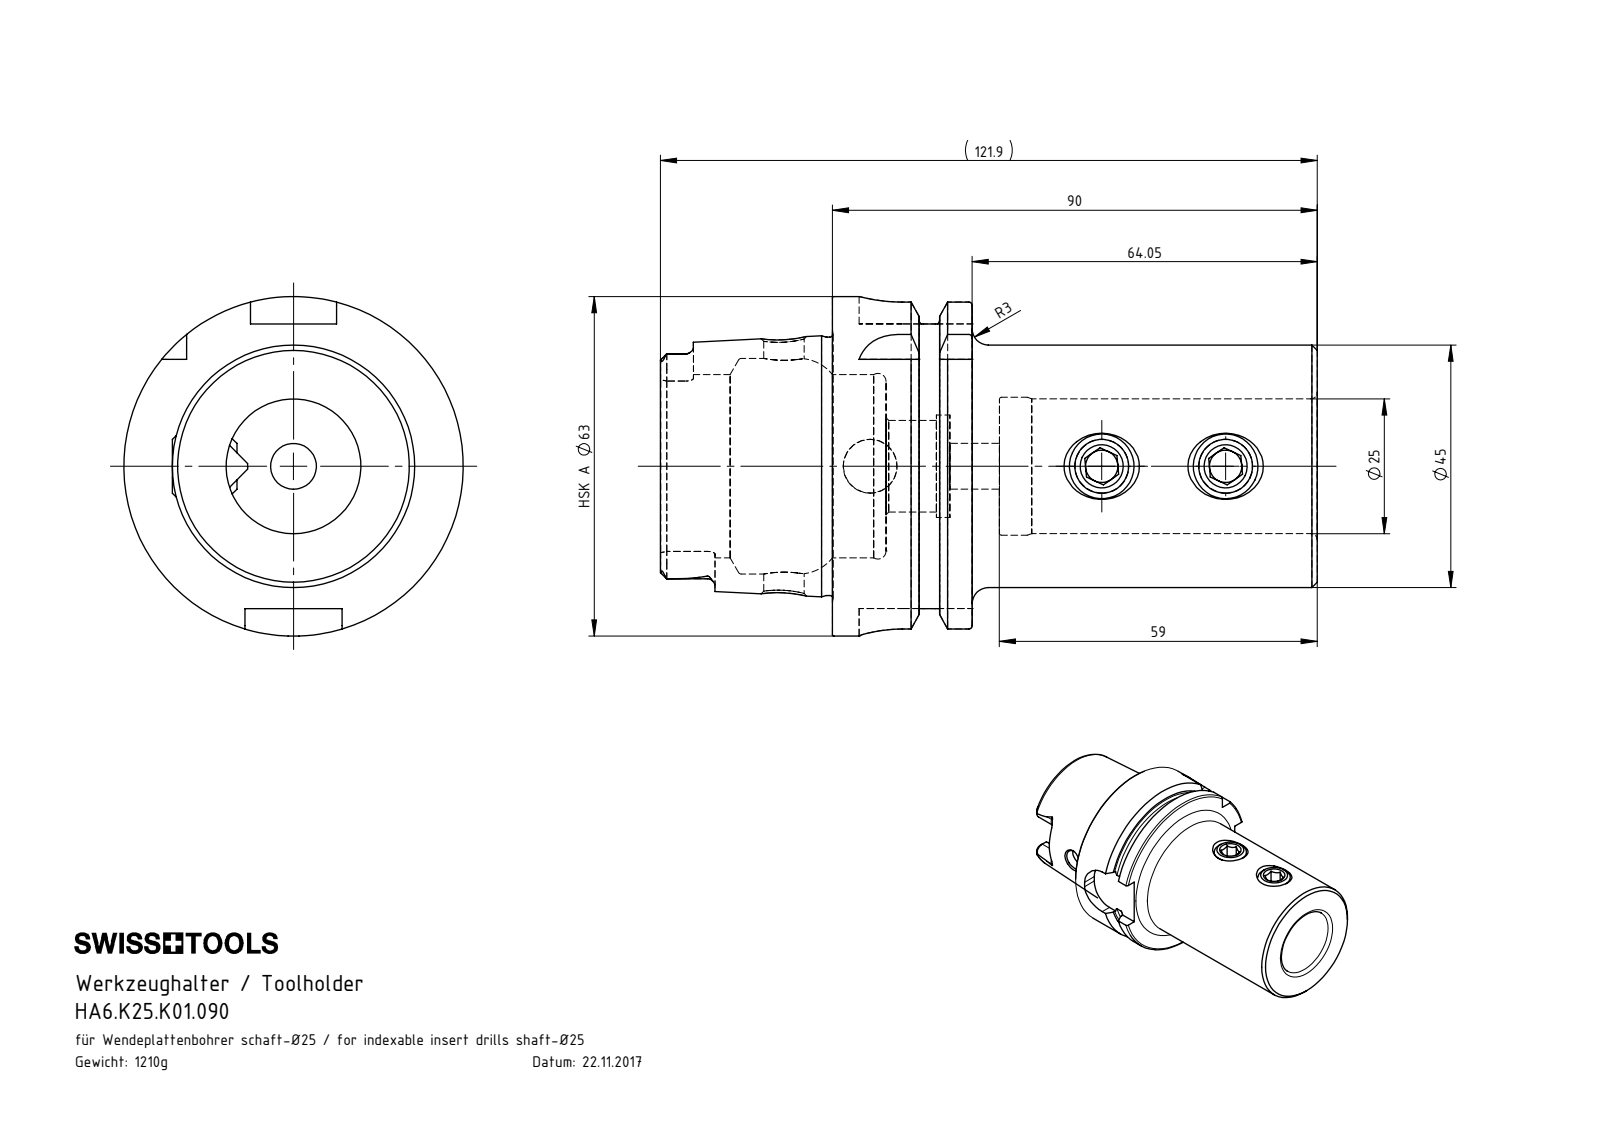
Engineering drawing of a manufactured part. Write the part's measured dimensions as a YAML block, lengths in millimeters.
part_name: "HA6-K25.K01.090_A_Fertigbearbeitung; HA6.K25.K01.090; K32-ER1.012.012; K32-ER2.012.014_PreviewCfg"
step_written_by: "SolidWorks 2017 (AUTOMOTIVE_DESIGN)"
units: millimeters
bodies: {solids: 3, faces: 227, planar: 75, cylindrical: 61, other: 91}
overall_size: [121.9, 63, 63]
volume: 153835
surface_area: 37565
round_holes:
  - {diameter: 6, count: 2}
  - {diameter: 11, count: 2}
  - {diameter: 7.5, count: 1}
  - {diameter: 8.5, count: 1}
  - {diameter: 10, count: 1}
  - {diameter: 17, count: 1}
  - {diameter: 19, count: 1}
  - {diameter: 25, count: 1}
  - {diameter: 25.6, count: 1}
  - {diameter: 34, count: 1}
  - {diameter: 40, count: 1}
round_bosses_or_shafts:
  - {diameter: 12, count: 2}
  - {diameter: 63, count: 1}
  - {diameter: 54.95, count: 1}
  - {diameter: 47.93, count: 1}
  - {diameter: 45, count: 1}
partial_cylinders:
  - {radius: 1.4, count: 6}
  - {radius: 2.88, count: 4}
  - {radius: 8, count: 4}
face_to_face_distances: [90, 25.95, 64.05, 16, 9.95, 80.05, 31, 21.05, 5.05, 59]
hole_center_spacings: [23, 43, 66]
